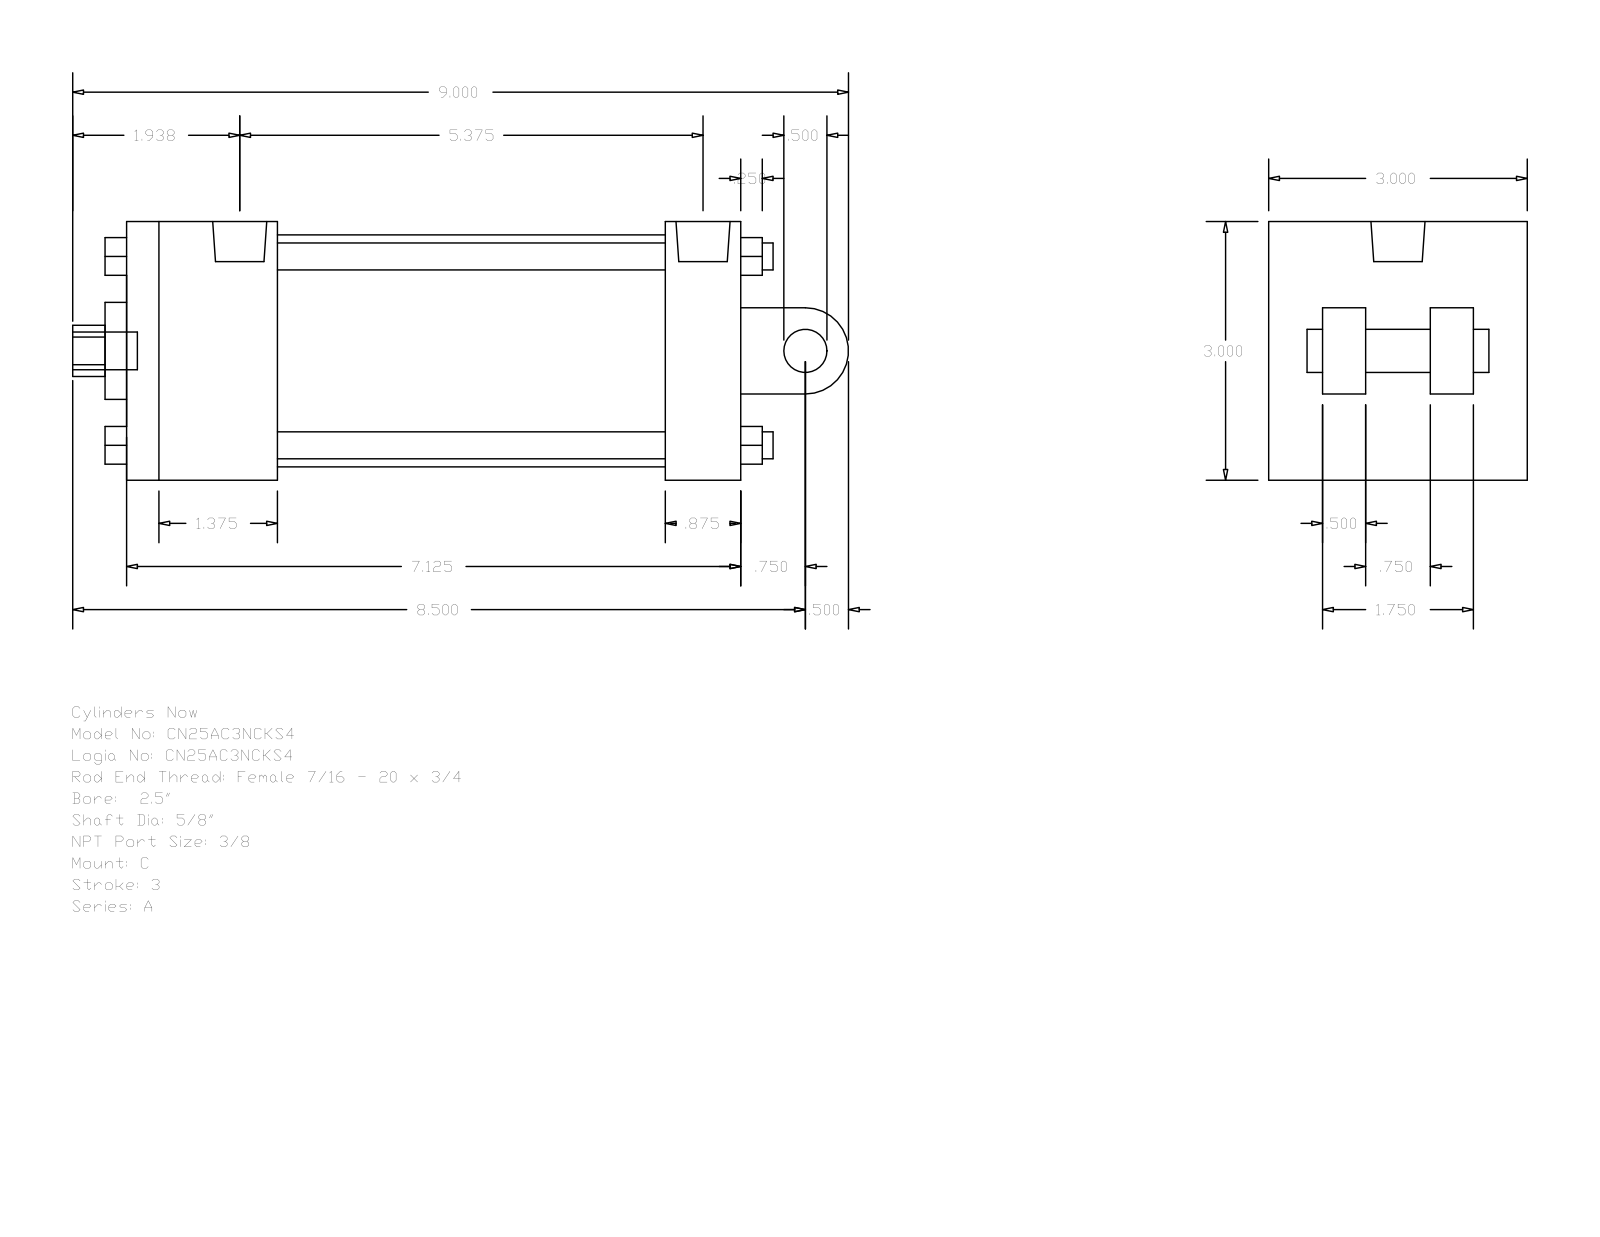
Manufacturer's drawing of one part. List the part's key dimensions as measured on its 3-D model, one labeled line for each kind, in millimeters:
Part name (STEP PRODUCT): A_C__0250_0.625
STEP written by: GSSL Pune (CONFIG_CONTROL_DESIGN)
Units: millimetres
Bodies: 0 solids, 135 faces (102 planar, 33 cylindrical, 0 other)
Overall size (bounding box): 228.6 × 76.2 × 76.2
Round holes (diameter × count): ⌀5.56 ×2, ⌀15.88 ×1, ⌀15.93 ×1, ⌀28.57 ×1, ⌀68.33 ×1
Round bosses / shafts (diameter × count): ⌀7.94 ×4, ⌀5.56 ×2, ⌀15.93 ×1, ⌀12.7 ×1, ⌀11.11 ×1
Partial cylindrical surfaces — rounded edges, fillets, slot ends (radius × count): R7.54 ×1, R12.7 ×1
Main face-to-face distances: 76.2, 180.97, 44.45, 158.74, 114.29, 136.52, 22.23, 50.8, 12.7, 15.87
Hole centre spacings: 2.38
